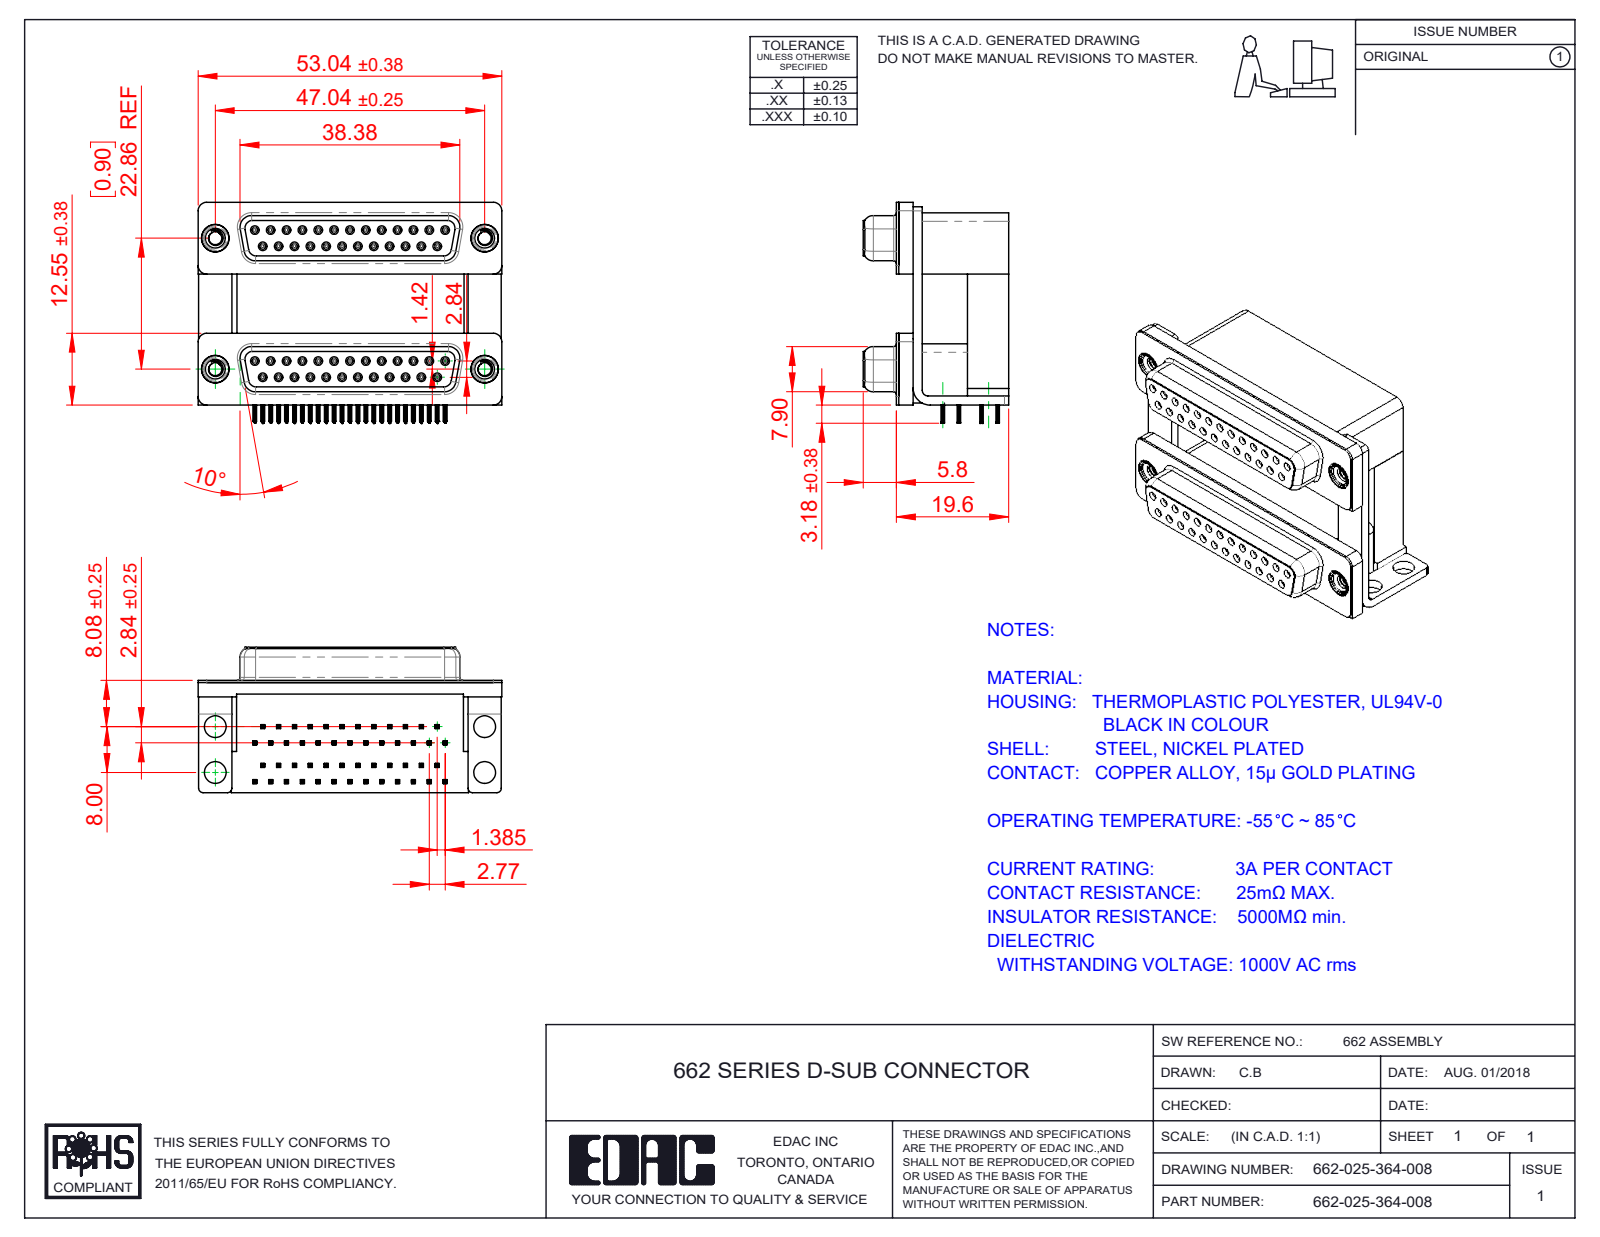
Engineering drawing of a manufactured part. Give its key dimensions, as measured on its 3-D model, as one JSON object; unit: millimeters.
{"part_name": "662 Contact Bottom Lower; 662 Mounting Bracket_NoneH; 662 Contact Top Upper_H; 662 Housing Upper_25 Contacts H (+7 more)", "step_written_by": "SolidWorks 2020 (CONFIG_CONTROL_DESIGN)", "units": "millimeters", "bodies": {"solids": 61, "faces": 7792, "planar": 3576, "cylindrical": 1804, "other": 2412}, "overall_size": [53.04, 38.59, 25.4], "volume_mm3": 24966, "surface_area_mm2": 26849, "round_holes": [[0.8, 50], [0.9, 50], [2.26, 4], [3.5, 4], [3.8, 4], [4, 4], [4.8, 4], [5, 4]], "round_bosses_or_shafts": [[1.2, 50], [4.9, 4], [4.75, 4], [3.9, 4]], "partial_cylinders_radius": [[0.1, 400], [0.15, 200], [0.35, 100], [0.34, 50], [0.28, 24], [1.35, 16], [1.5, 14], [0.5, 8]], "face_to_face_distances": [22.86, 19.2, 7.2, 12, 0.4, 10.7, 2.84, 6.2, 9.5, 16.7], "hole_center_spacings": [3.16, 2.77, 5.54, 11.08, 8.31, 5.03, 13.85, 7.48]}
